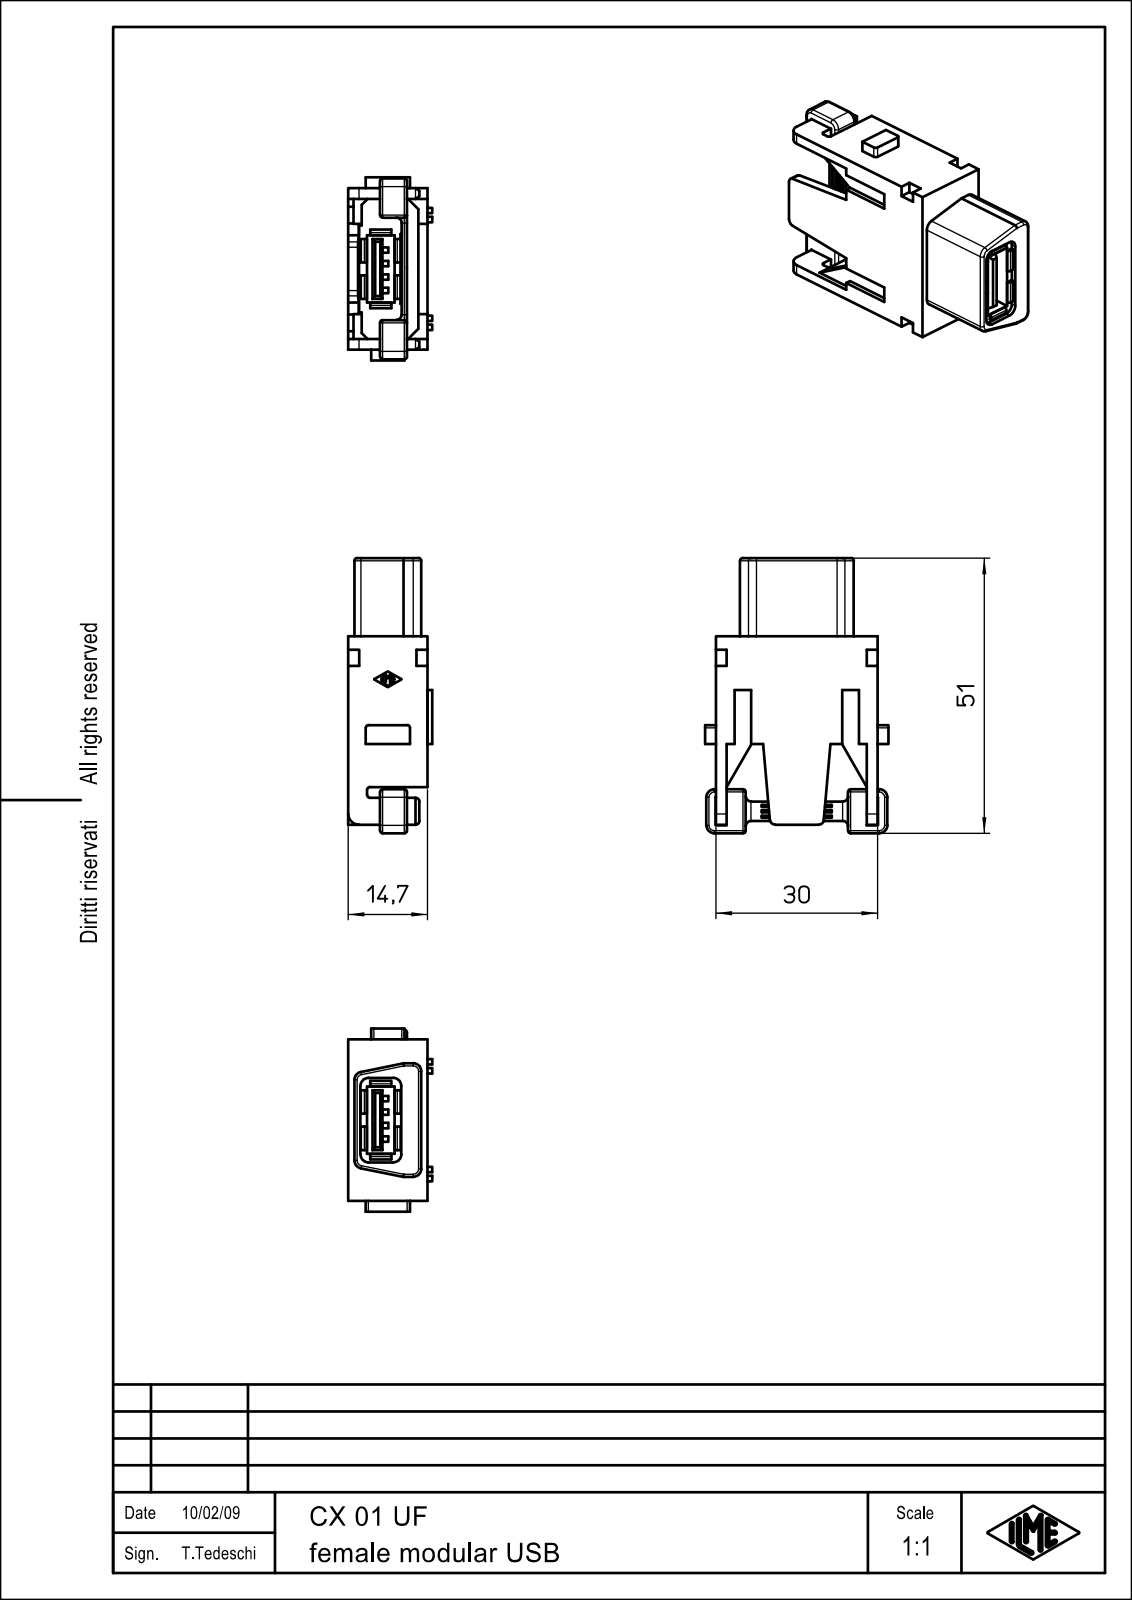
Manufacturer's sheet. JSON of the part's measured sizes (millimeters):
{"part_name": "CX_01_UF", "step_written_by": "CoCreate Modeling 16.00A 16-Aug-2008 (C) Parametric Technology GmbH (AUTOMOTIVE_DESIGN)", "units": "millimeters", "bodies": {"solids": 1, "faces": 469, "planar": 315, "cylindrical": 102, "other": 52}, "overall_size": [51.1, 34, 15.6], "volume_mm3": 11668, "surface_area_mm2": 7572, "partial_cylinders_radius": [[0.5, 30], [0.1, 14], [1, 10], [1.5, 10], [0.2, 2], [0.7, 2], [1.8, 2], [2, 1]], "face_to_face_distances": [14.7, 30, 13.55, 1.15, 28, 2, 6.1, 8.6, 7.45, 5.12]}
